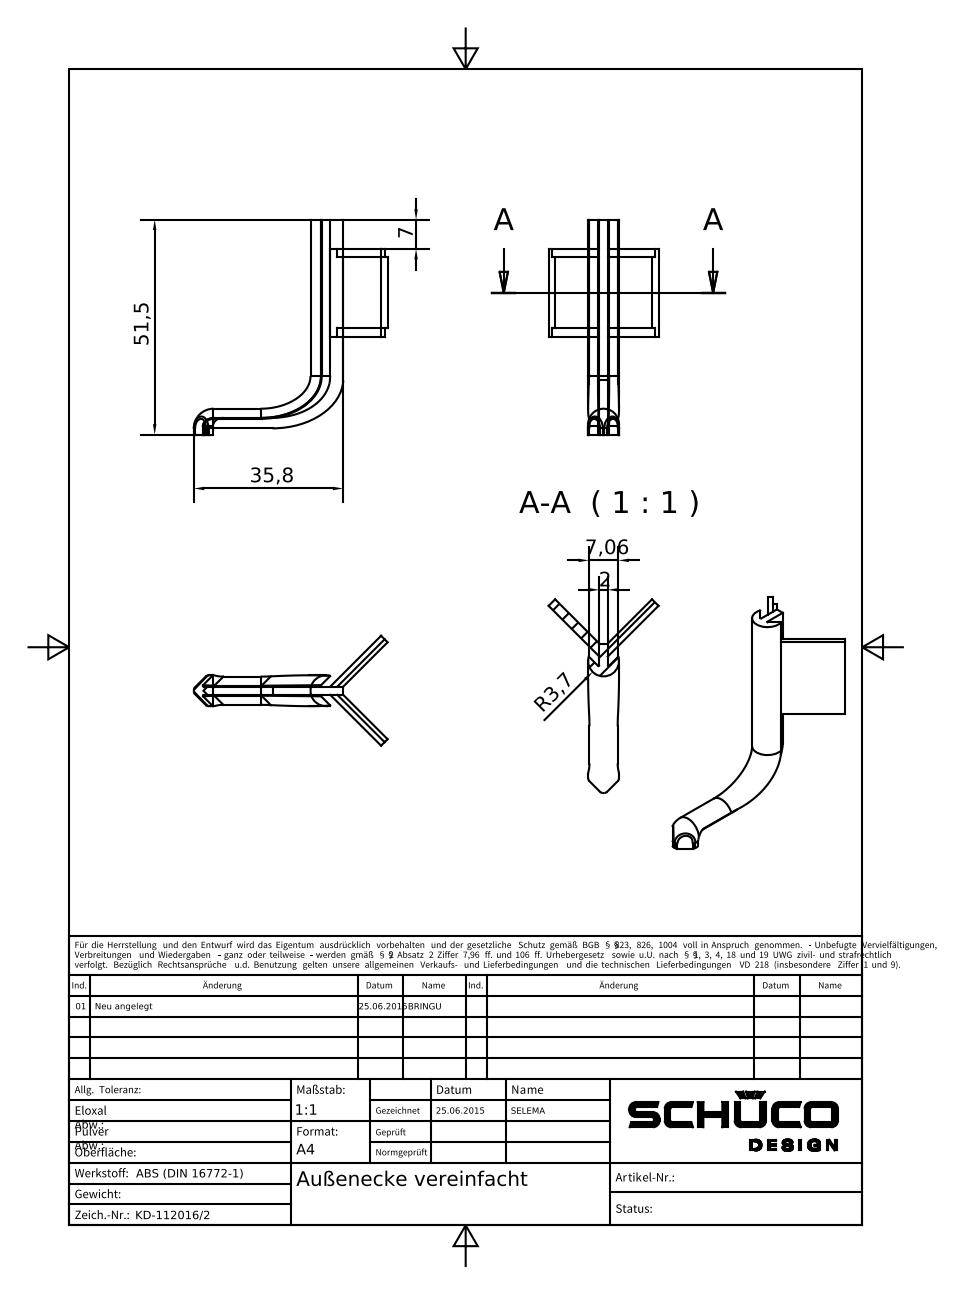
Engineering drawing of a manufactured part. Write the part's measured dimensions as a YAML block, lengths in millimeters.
part_name: "KD-112016"
step_written_by: "Autodesk Inventor 2024 (AUTOMOTIVE_DESIGN)"
units: millimeters
bodies: {solids: 1, faces: 67, planar: 36, cylindrical: 20, other: 11}
overall_size: [51.5, 46.42, 26.32]
volume: 3164
surface_area: 3661
partial_cylinders:
  - {radius: 0.2, count: 7}
  - {radius: 1, count: 4}
  - {radius: 3.7, count: 3}
  - {radius: 2, count: 2}
  - {radius: 10, count: 2}
face_to_face_distances: [2.2, 2, 4, 1.8, 1, 1.2, 3, 16.41, 17.41, 18.61]
